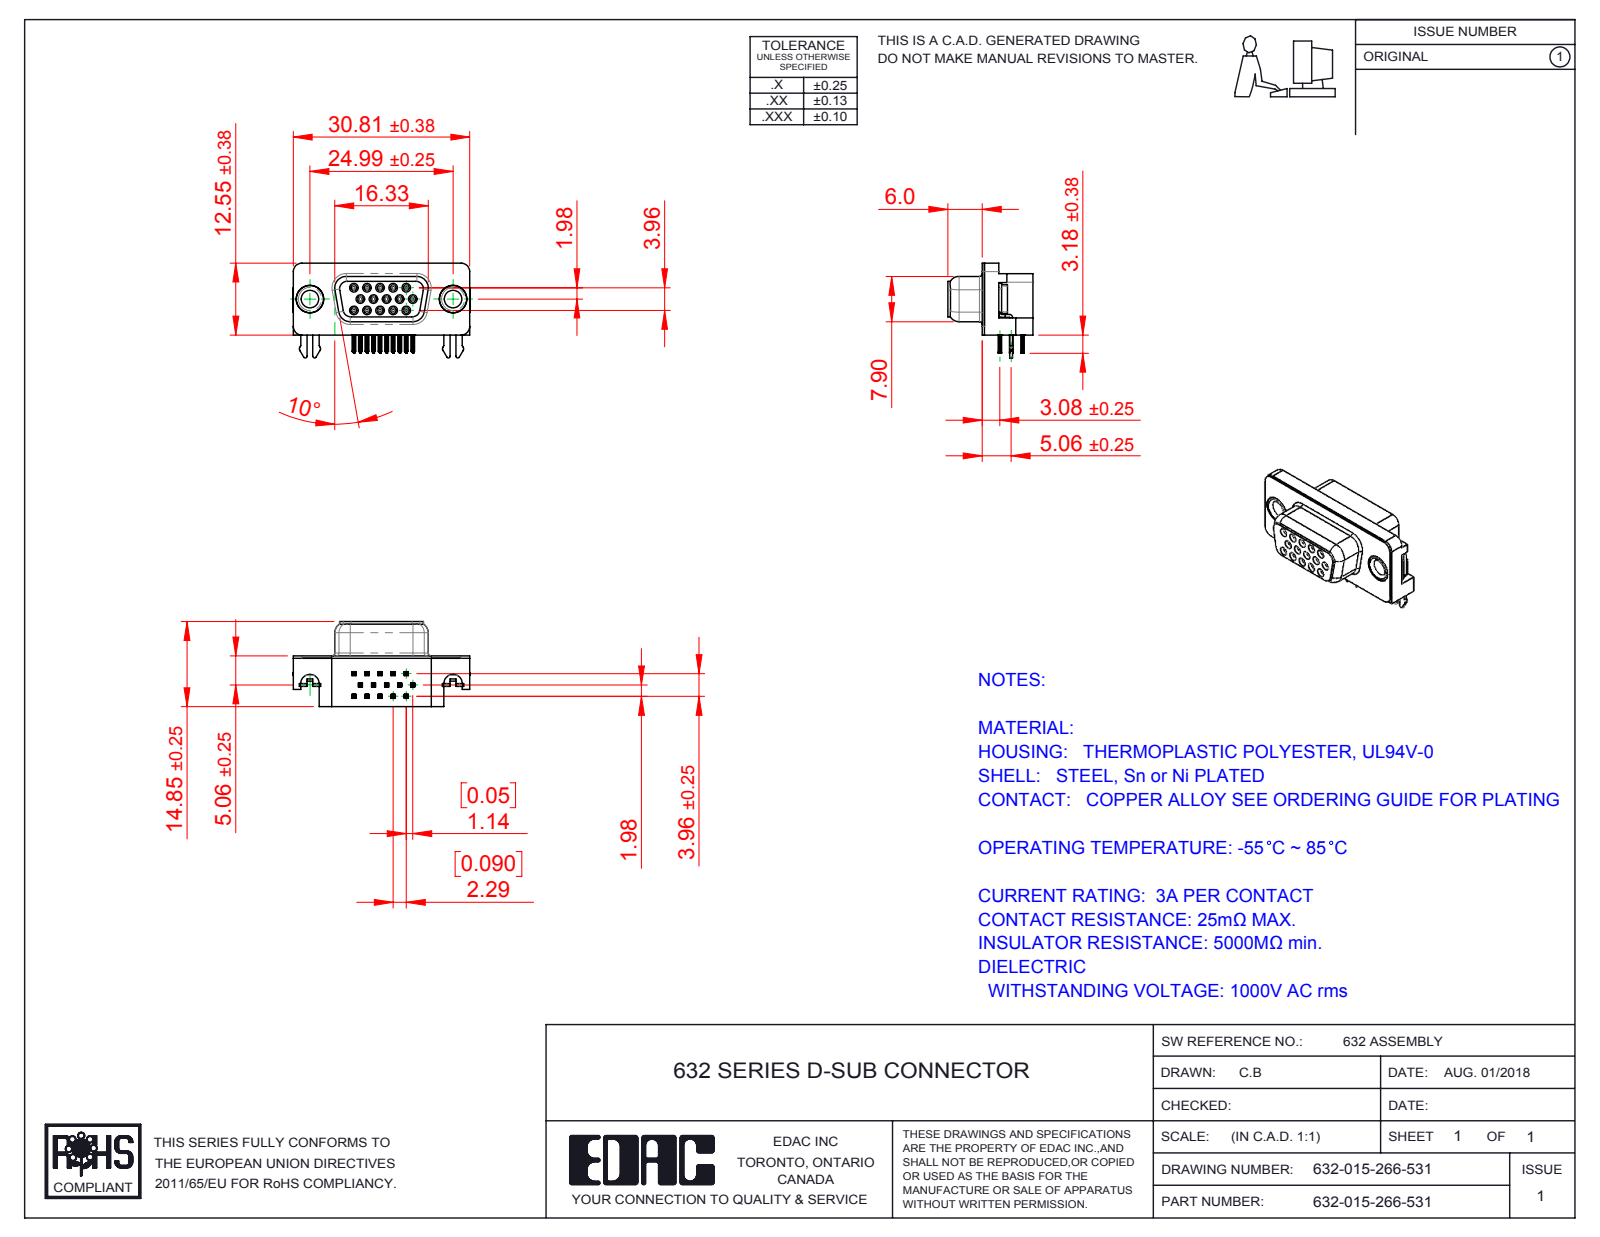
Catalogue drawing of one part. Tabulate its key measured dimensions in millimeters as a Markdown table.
| quantity | value |
| --- | --- |
| part name | 632-015-266-501; 632 Housing_15 Socket; 632 Contact Middle; 632 Contact Bottom (+4 more) |
| STEP written by | SolidWorks 2016 (CONFIG_CONTROL_DESIGN) |
| units | millimeters |
| bodies | 21 solids, 2298 faces (990 planar, 594 cylindrical, 714 other) |
| overall size | 30.89 × 16.55 × 14.85 |
| volume | 2 908 mm³ |
| surface area | 4 994 mm² |
| round holes (diameter × count) | 0.8 × 15, 0.9 × 15, 3.05 × 2, 4 × 2, 4.8 × 2, 5 × 2 |
| round bosses / shafts (diameter × count) | 1.2 × 15, 4.9 × 2, 4.75 × 2, 3.85 × 2 |
| partial cylindrical surfaces (radius × count) | 0.1 × 120, 0.15 × 60, 0.35 × 30, 0.34 × 15, 1 × 11, 0.28 × 10, 0.5 × 10, 0.25 × 8 |
| main face-to-face distances | 0.4, 1.98, 8.45, 8.85, 2.9, 2.5, 5.95, 6.4, 6.7, 7.05 |
| hole center spacings | 2.28, 2.29, 3.96, 4.57, 6.05, 3.97, 4.58, 6.86 |
